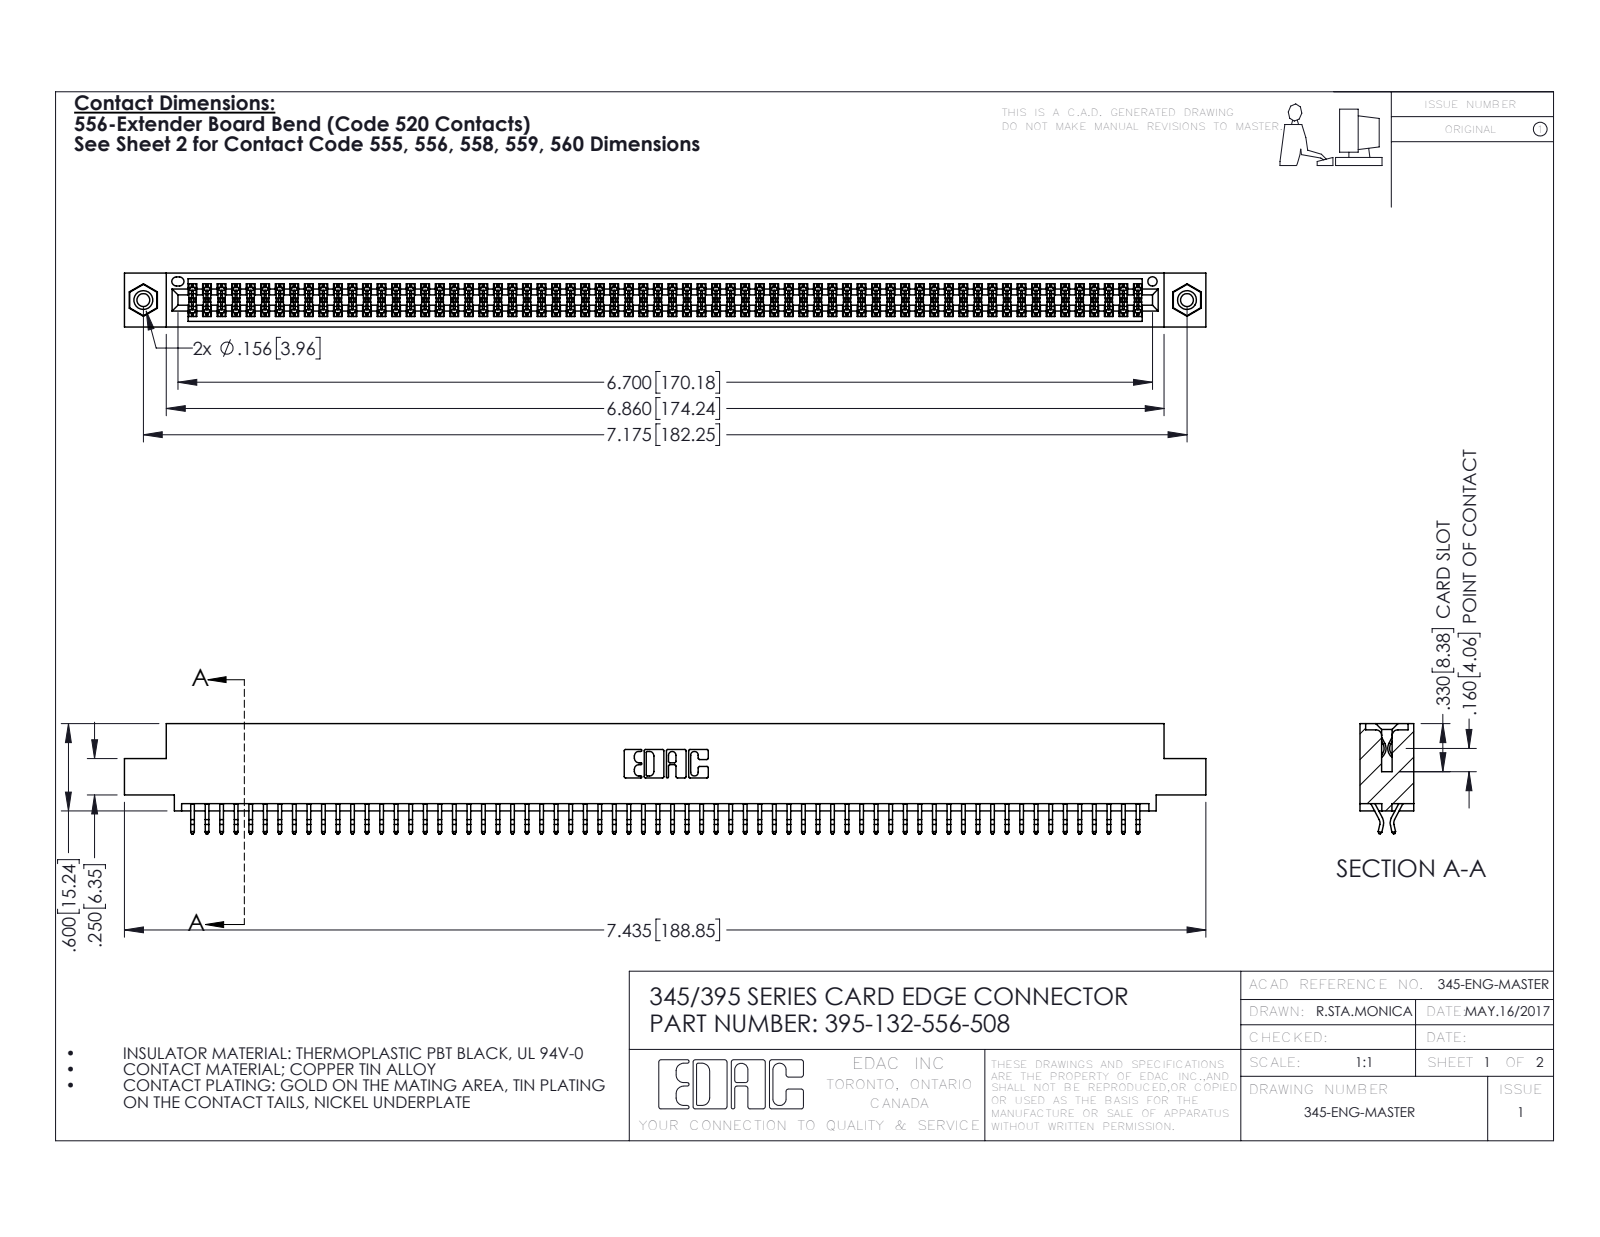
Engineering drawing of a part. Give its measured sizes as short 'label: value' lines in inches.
name: 395-132-556-508; 345 Part_0.110 Offset - 0.156 Dia-TI; 345-250-001_345-250-003-102; 345-292-001_556 Tail
written by: SolidWorks 2016 (CONFIG_CONTROL_DESIGN)
unit: in
bodies: 135 solids, 7582 faces (5000 planar, 2566 cylindrical, 16 other)
size: 7.435 × 0.757 × 0.37
volume: 1.128 in³; area: 43.05 in²
holes: 2× ⌀0.089, 2× ⌀0.125, 2× ⌀0.156, 1× ⌀0.064
bosses: 2× ⌀0.155
rounds: 198× R0.006, 22× R0.01, 6× R0.007, 6× R0.031, 3× R0.026, 2× R0.01, 2× R0.014, 2× R0.019
face distances: 0.072, 0.298, 0.37, 0.2, 0.025, 0.098, 0.272, 0.225, 0.175, 0.149
hole spacings: 0.27, 6.939, 7.175
